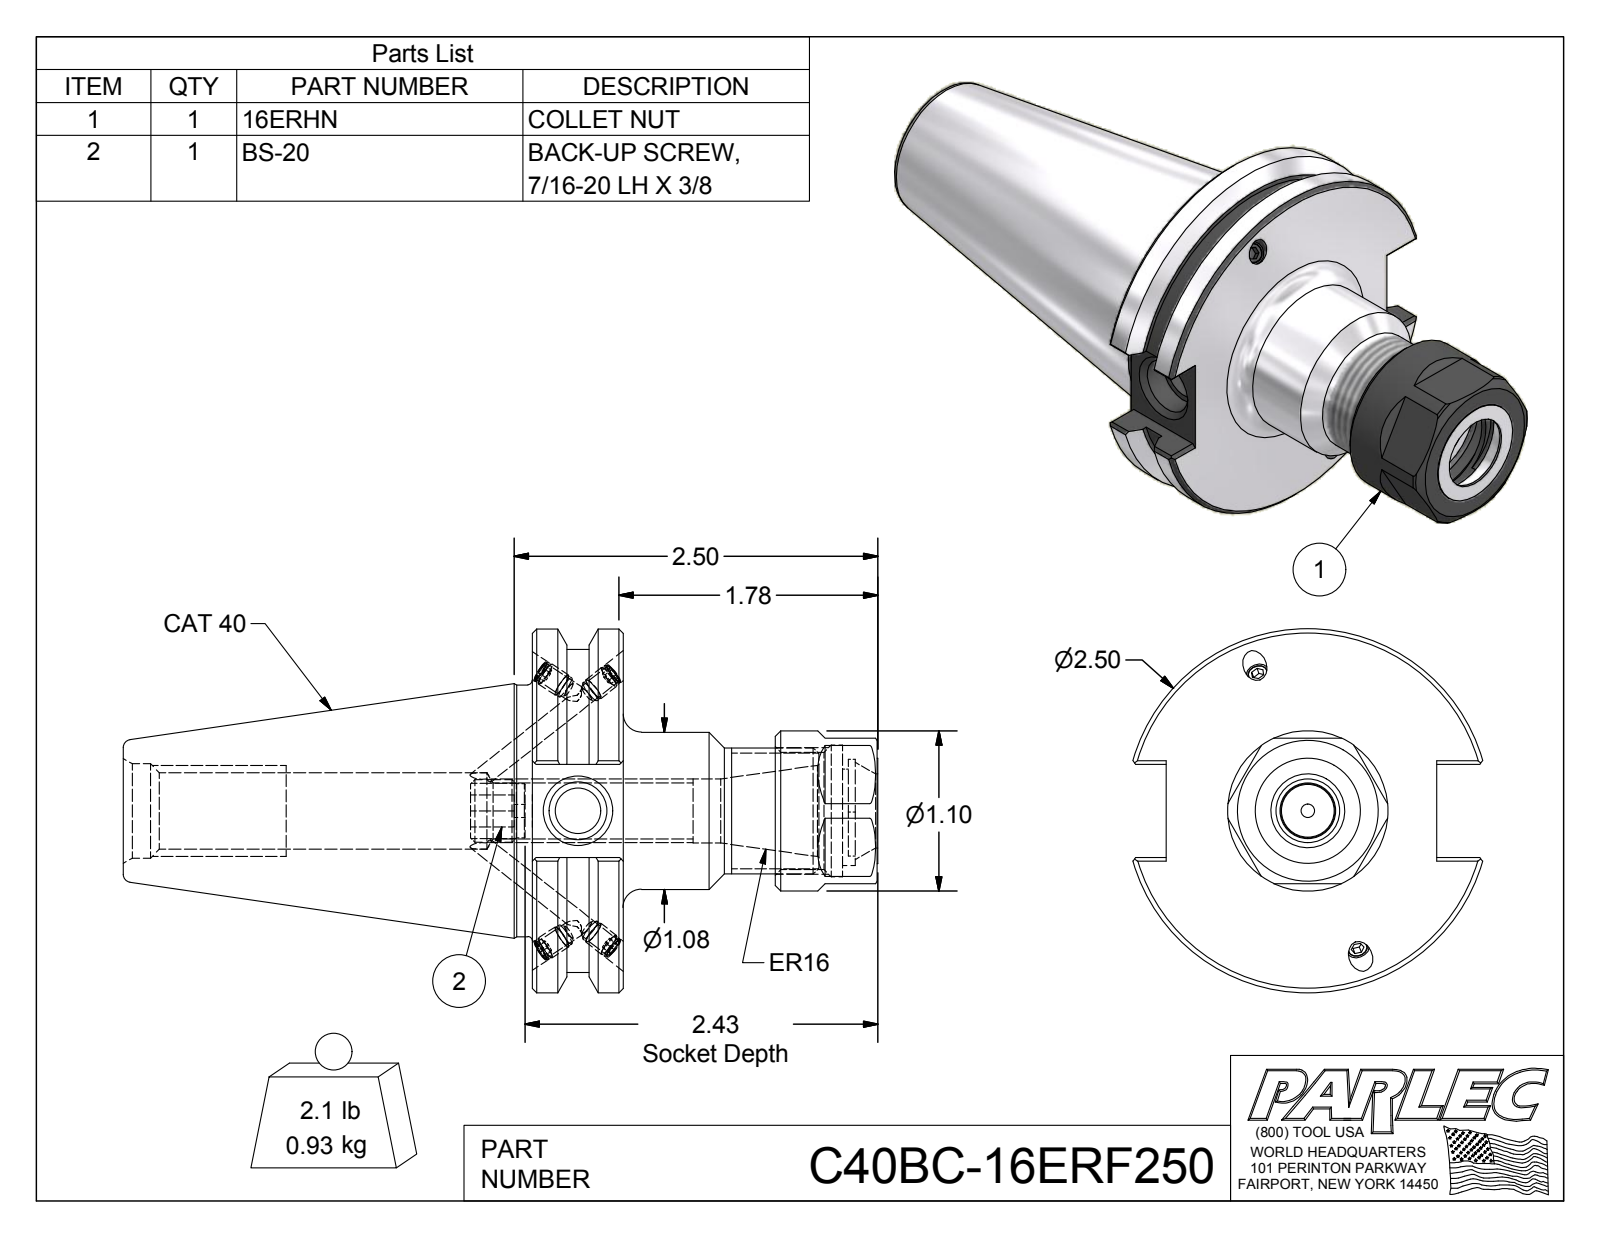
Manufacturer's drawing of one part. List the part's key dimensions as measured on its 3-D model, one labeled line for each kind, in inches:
Part name (STEP PRODUCT): C40BCB-16ER2-1; 029-965; 16ERHN; BS-20 (+1 more)
STEP written by: Autodesk Inventor 2016 (AUTOMOTIVE_DESIGN)
Units: inches
Bodies: 7 solids, 199 faces (102 planar, 45 cylindrical, 52 other)
Overall size (bounding box): 5.187 × 2.5 × 2.404
Volume: 7.294 in³ · Surface area: 44.92 in²
Round holes (diameter × count): ⌀0.13 ×4, ⌀0.161 ×4, ⌀0.09 ×1, ⌀0.315 ×1, ⌀0.383 ×1, ⌀0.396 ×1, ⌀0.44 ×1, ⌀0.488 ×1, ⌀0.527 ×1, ⌀0.648 ×1, ⌀0.67 ×1, ⌀0.807 ×1
Round bosses / shafts (diameter × count): ⌀0.165 ×4, ⌀0.157 ×4, ⌀2.5 ×1, ⌀2.219 ×1, ⌀1.73 ×1, ⌀1.102 ×1, ⌀1.08 ×1, ⌀0.866 ×1
Partial cylindrical surfaces — rounded edges, fillets, slot ends (radius × count): R0.285 ×1, R0.354 ×1
Main face-to-face distances: 0.625, 2.375, 1.75, 0.99, 0.175, 0.815, 2.151, 1.526, 0.224, 0.64
Hole centre spacings: 0.06
